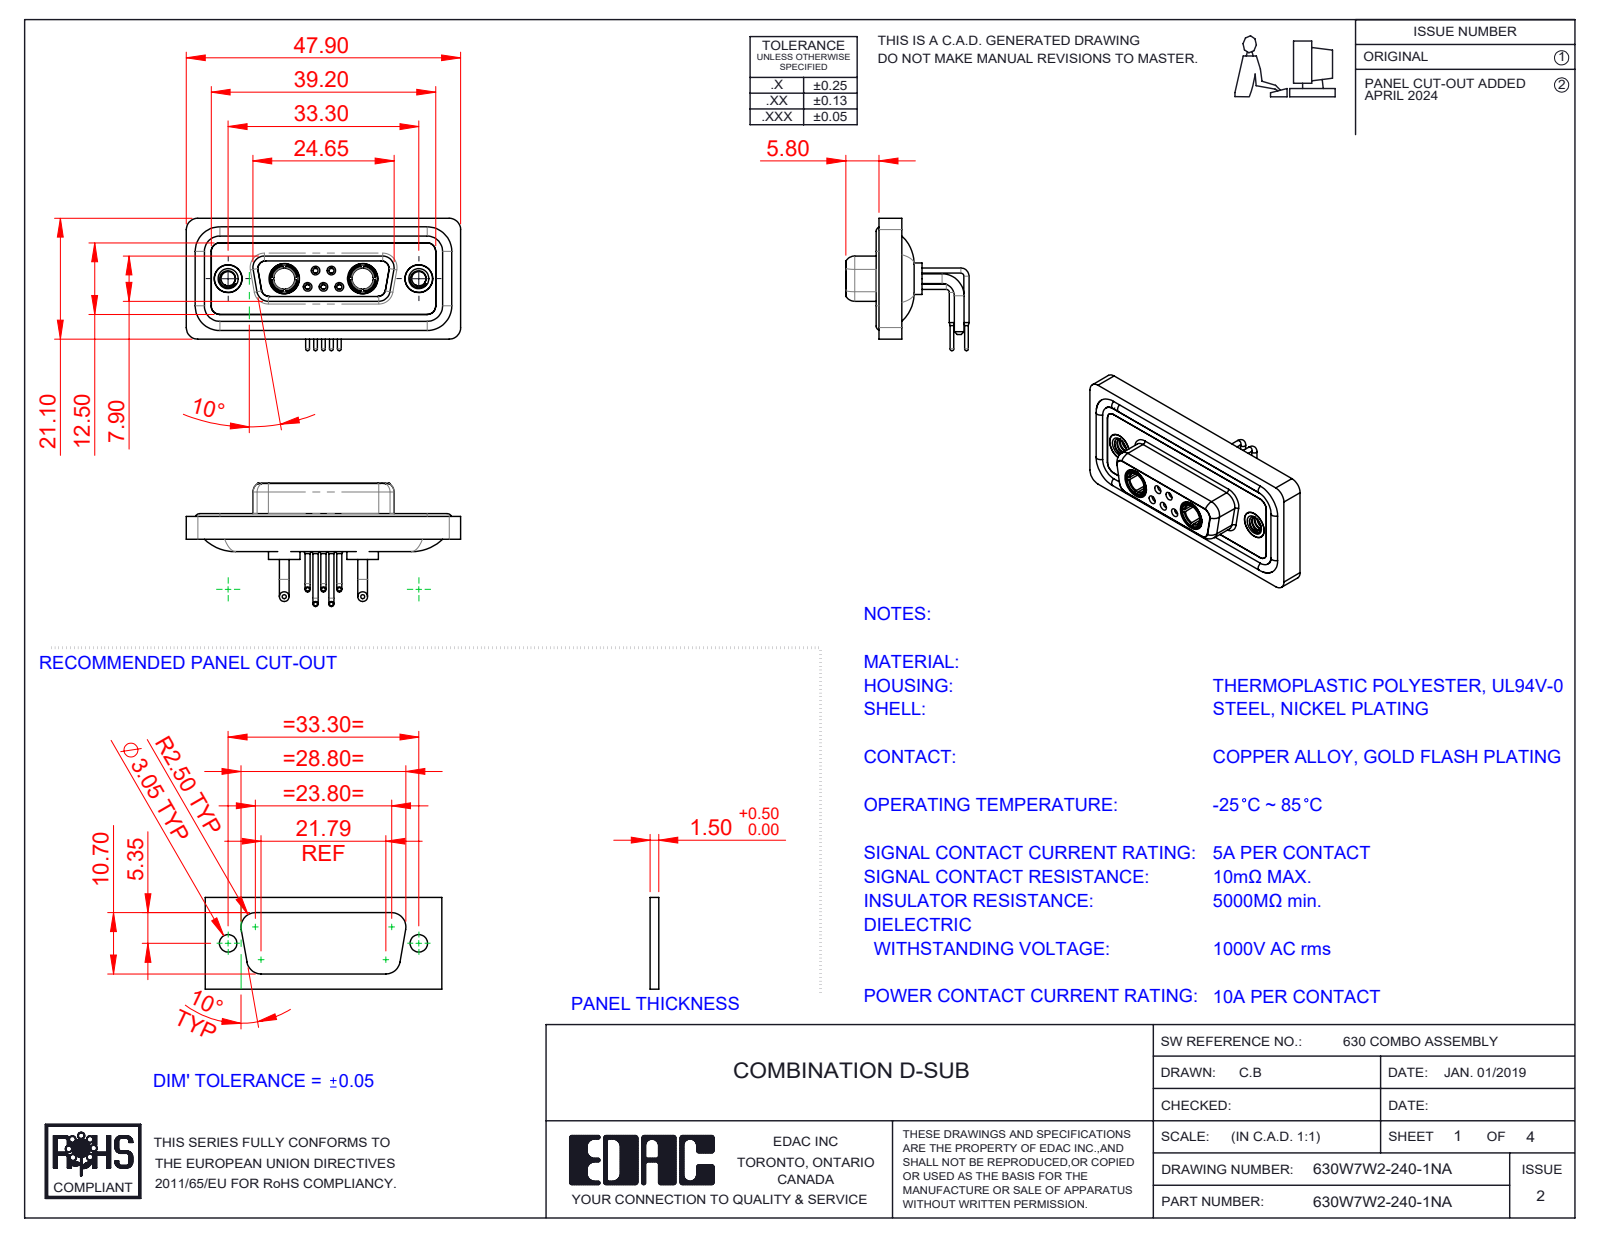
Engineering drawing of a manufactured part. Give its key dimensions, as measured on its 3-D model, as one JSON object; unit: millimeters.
{"part_name": "630Combo Contact Row 1_50 Contacts; 630Combo Shell Rear_15 Contacts; 630Combo Contact Row 2_50 Contacts; 630Combo Housing_7W2 (+5 more)", "step_written_by": "SolidWorks 2023 (CONFIG_CONTROL_DESIGN)", "units": "millimeters", "bodies": {"solids": 16, "faces": 801, "planar": 238, "cylindrical": 351, "other": 212}, "overall_size": [47.9, 23.12, 21.53], "volume_mm3": 6073, "surface_area_mm2": 10107, "round_holes": [[0.9, 5], [1.1, 5], [1.5, 5], [2, 5], [4.85, 4], [1.6, 3], [1.7, 2], [2.5, 2], [3.7, 2], [4, 2], [4.05, 2], [5, 2]], "round_bosses_or_shafts": [[1.6, 6], [0.9, 5], [0.65, 5], [1.7, 4], [5.5, 2], [5.2, 2], [4.96, 2], [4.95, 2]], "partial_cylinders_radius": [[2, 20], [1.5, 18], [1.35, 12], [1.6, 8], [0.25, 4], [0.5, 4], [0.6, 4], [0.65, 4]], "face_to_face_distances": [0.4, 1.8, 1.1, 1.6, 2.9, 2.5, 3.1, 3.7, 4.1, 1.5], "hole_center_spacings": [3.16, 2.77, 9.8, 23.5, 4.31, 4.33, 5.03, 5.04]}
